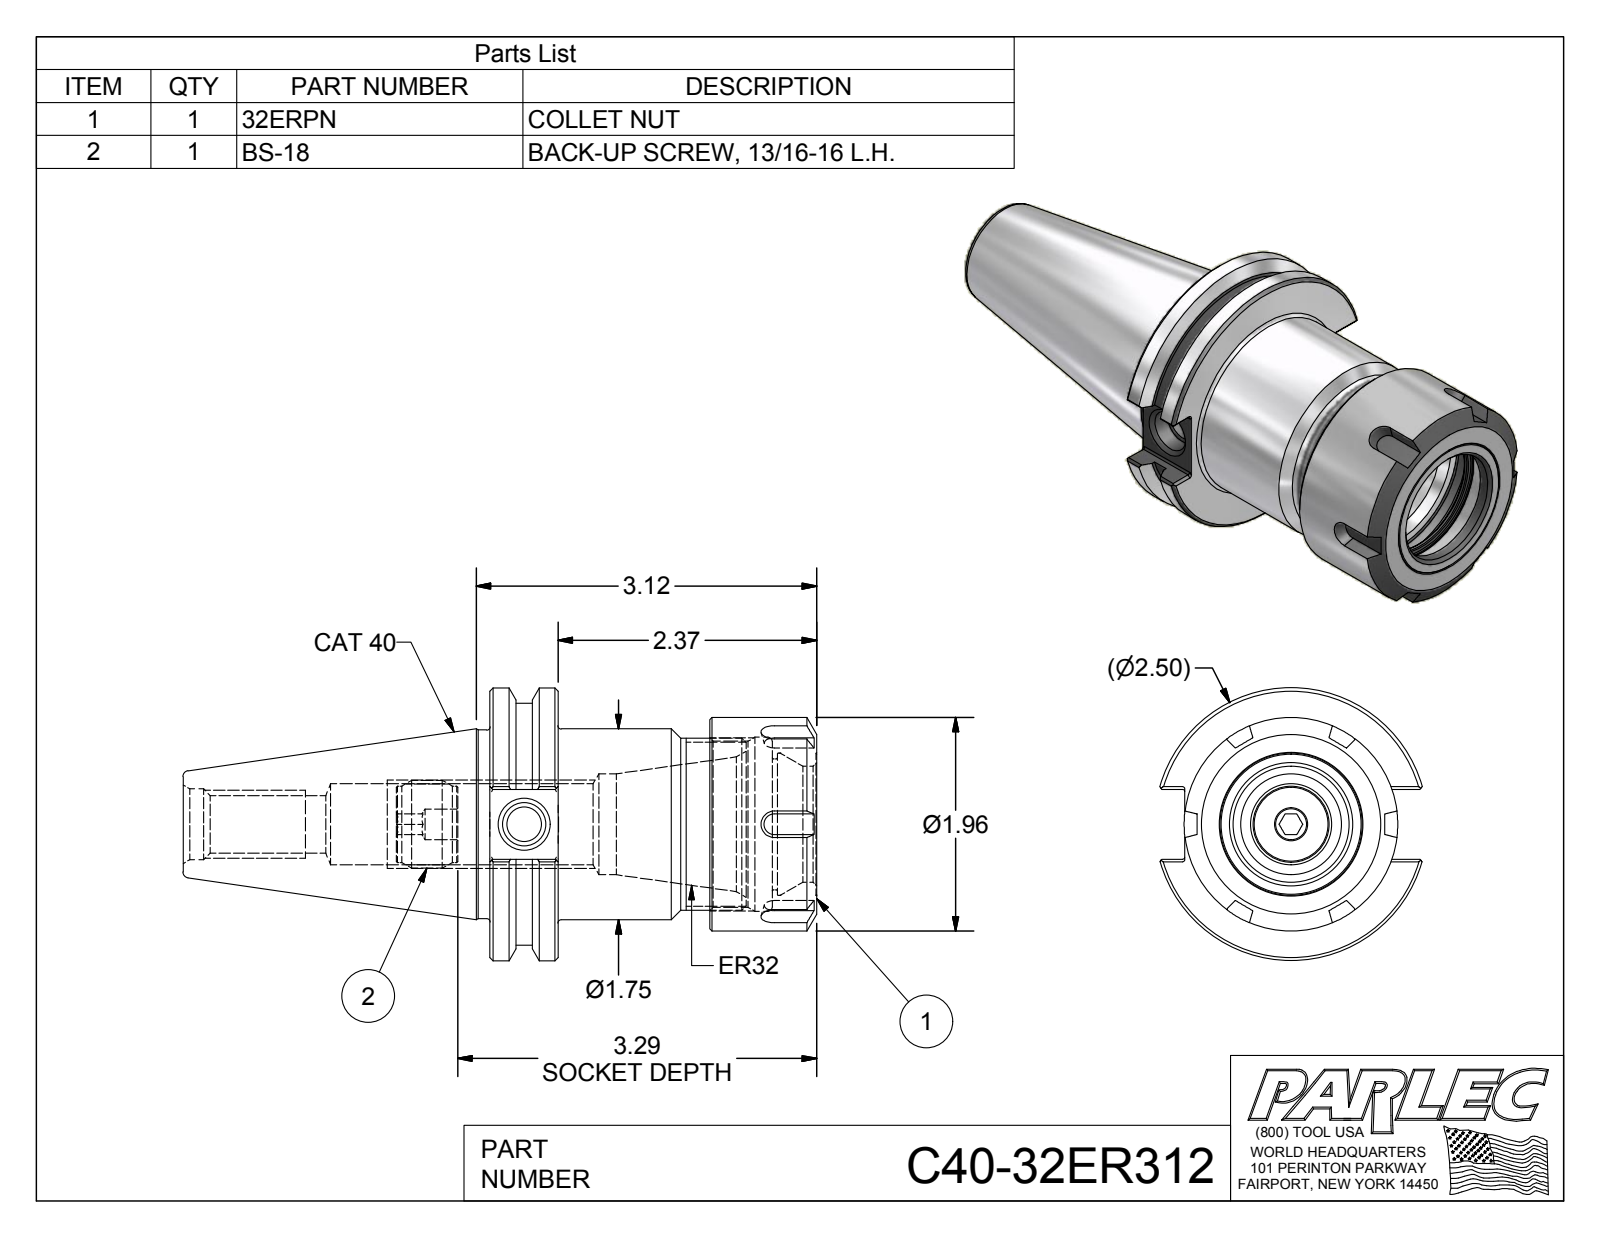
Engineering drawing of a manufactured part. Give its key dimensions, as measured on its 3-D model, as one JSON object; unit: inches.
{"part_name": "C40-32ER312; C40-32ER3-1; 32ERPN; BS-18", "step_written_by": "Autodesk Inventor 2012 (AUTOMOTIVE_DESIGN)", "units": "inches", "bodies": {"solids": 3, "faces": 148, "planar": 62, "cylindrical": 37, "other": 49}, "overall_size": [5.808, 2.5, 2.403], "volume_in3": 9.677, "surface_area_in2": 63.08, "round_holes": [[0.28, 1], [0.315, 1], [0.399, 1], [0.527, 1], [0.648, 1], [0.745, 1], [0.925, 1], [1.063, 1], [1.2, 1], [1.305, 1], [1.523, 1], [1.595, 1]], "round_bosses_or_shafts": [[2.5, 1], [2.219, 1], [1.958, 1], [1.75, 1], [1.73, 1], [1.575, 1], [0.805, 1], [0.7, 1]], "partial_cylinders_radius": [[0.02, 12]], "face_to_face_distances": [0.625, 2.995, 2.37, 2.017, 1.392, 0.978, 2.588, 1.963, 0.571, 0.407]}
